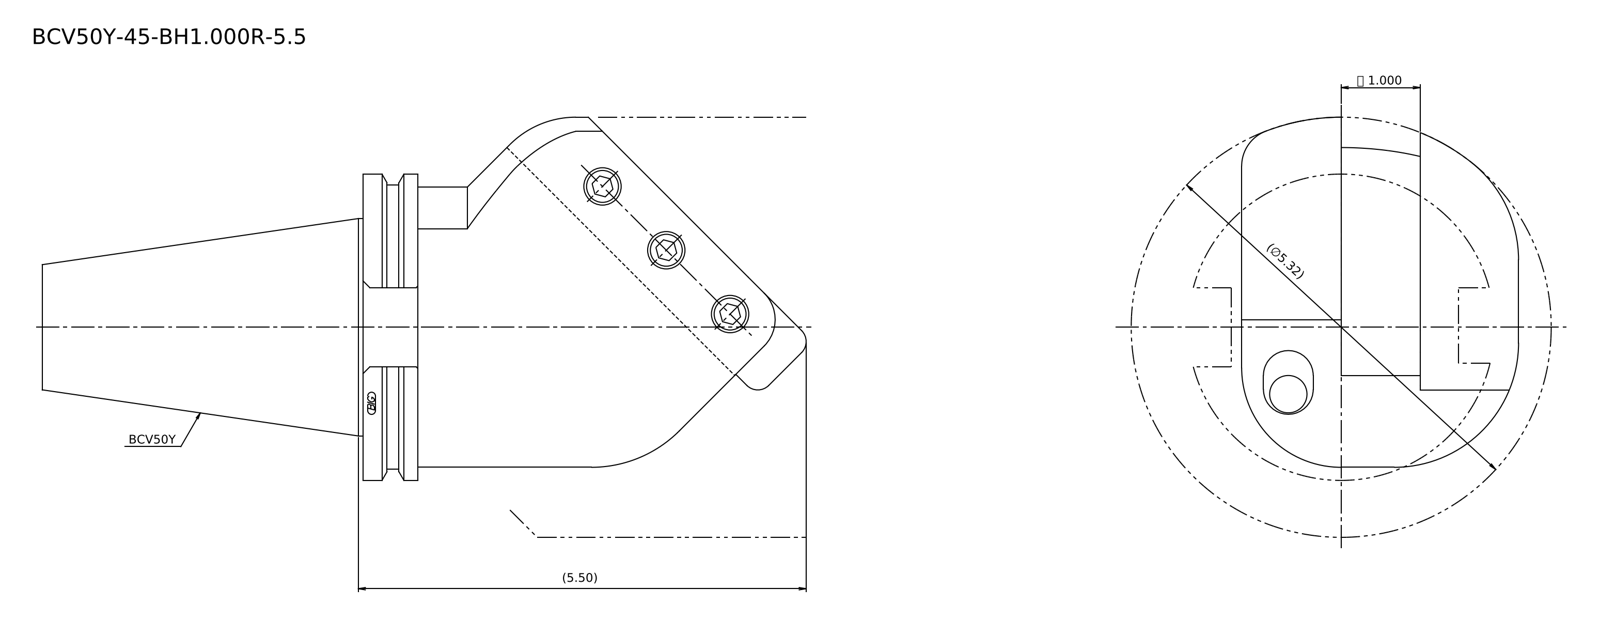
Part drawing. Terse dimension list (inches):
written by: Kubotek KeyCreator 2011 V10.0.2 (22737) (automotive_design)
unit: in
bodies: 1 solid, 31 faces (16 planar, 11 cylindrical, 4 other)
size: 9.748 × 4.595 × 4.181
volume: 65.3 in³; area: 119.4 in²
bosses: 1× ⌀3.875, 1× ⌀3.594, 1× ⌀2.75
rounds: 2× R1.575, 1× R0.472, 1× R1.26, 1× R1.772, 1× R2.657
face distances: 1, 2.26, 1.26, 3.504, 2.244, 1.244, 0.691, 4.75, 4.059, 0.393
